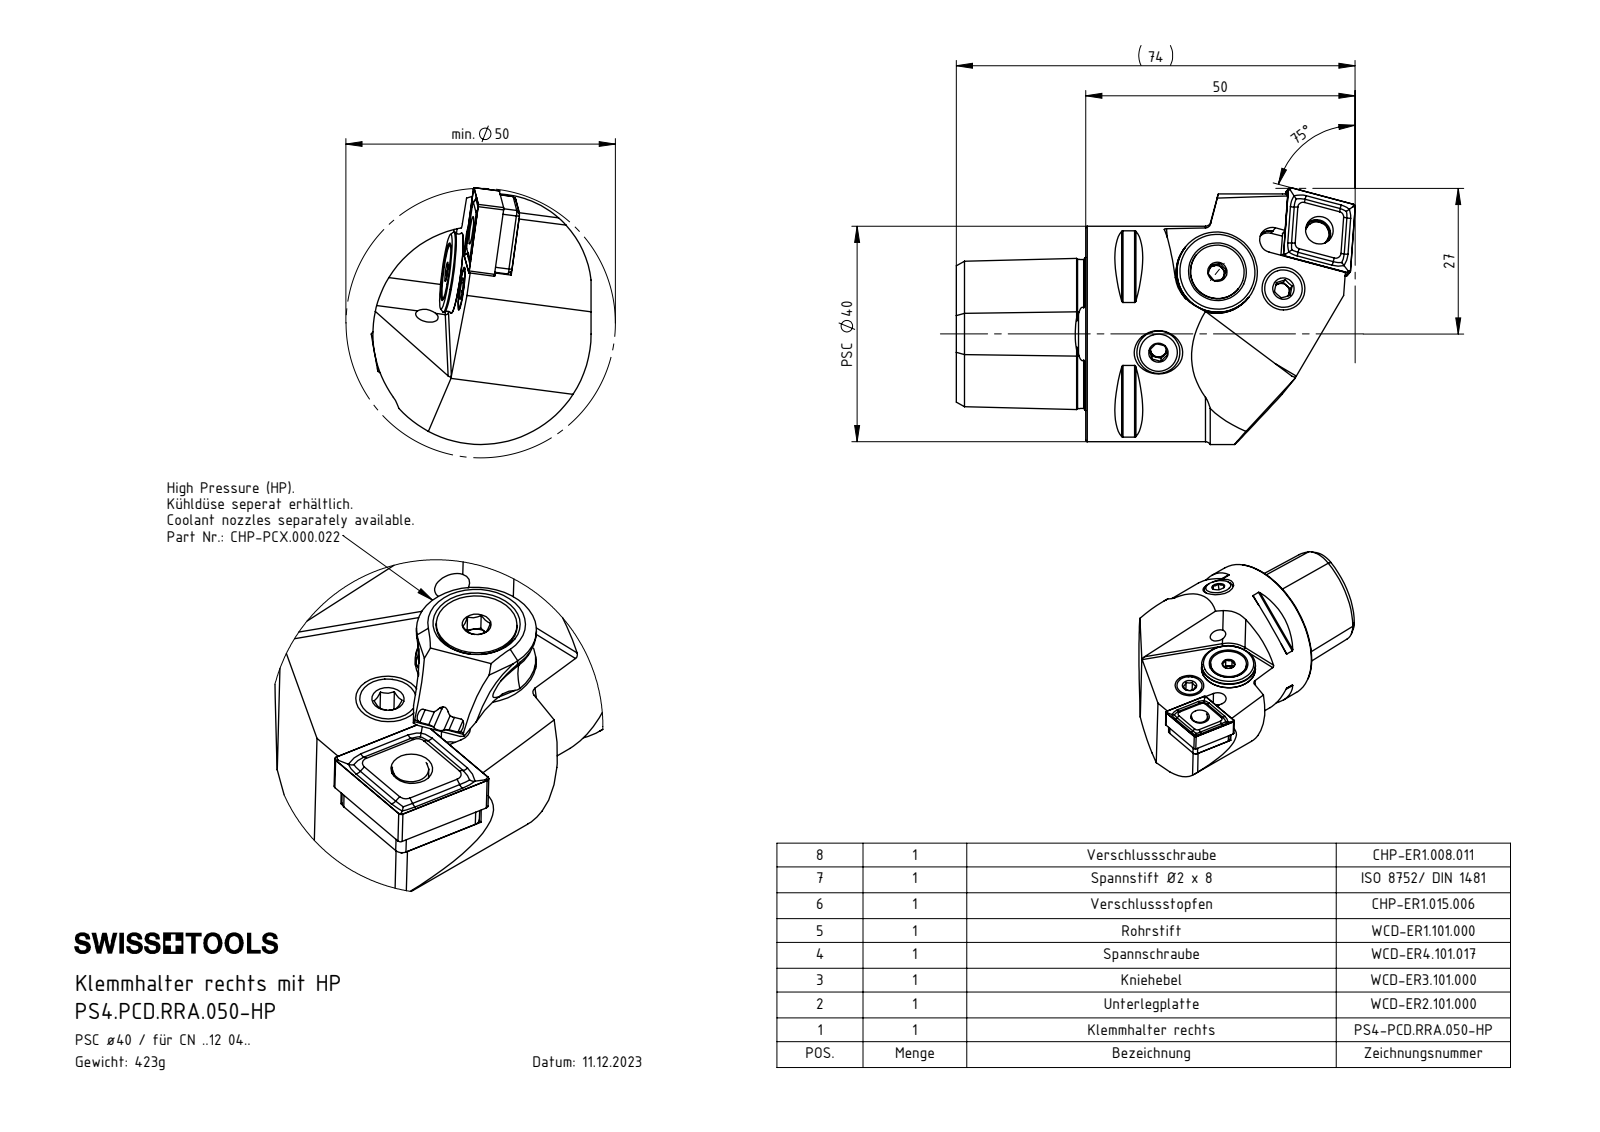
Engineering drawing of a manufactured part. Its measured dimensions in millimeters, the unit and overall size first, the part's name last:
Units: millimetres
Overall size (bounding box): 74.05 × 47.66 × 40.5
Round holes (diameter × count): ⌀4.2 ×2, ⌀7 ×2, ⌀1.2 ×1, ⌀2 ×1, ⌀3 ×1, ⌀3.3 ×1, ⌀4 ×1, ⌀4.6 ×1, ⌀5 ×1, ⌀5.16 ×1, ⌀5.3 ×1, ⌀6.55 ×1
Round bosses / shafts (diameter × count): ⌀8 ×2, ⌀40 ×1, ⌀14.85 ×1, ⌀13.4 ×1, ⌀10 ×1, ⌀7.9 ×1, ⌀6.4 ×1, ⌀5.5 ×1
Partial cylindrical surfaces — rounded edges, fillets, slot ends (radius × count): R1 ×11, R0.3 ×9, R0.4 ×4, R0.5 ×4, R6 ×3, R1.1 ×2, R1.2 ×2, R2.5 ×2
Main face-to-face distances: 11.8, 24, 4.5, 0.5, 3.13, 7.63, 3.17, 4.46, 3, 15.52
Hole centre spacings: 4.51, 12.83, 20.97, 4.5, 4.52, 12.63, 12.64, 12.85
Volume: 53 499 mm³ · Surface area: 18 206 mm²
Bodies: 12 solids, 558 faces (146 planar, 146 cylindrical, 266 other)
Part name (STEP PRODUCT): CHP-PCX.000.022_Düse; DIN 3771 - 6.5x1.5; DIN 3771 - 13x1; CNMG120404 (+8 more)
STEP written by: SolidWorks 2022 (AUTOMOTIVE_DESIGN)
